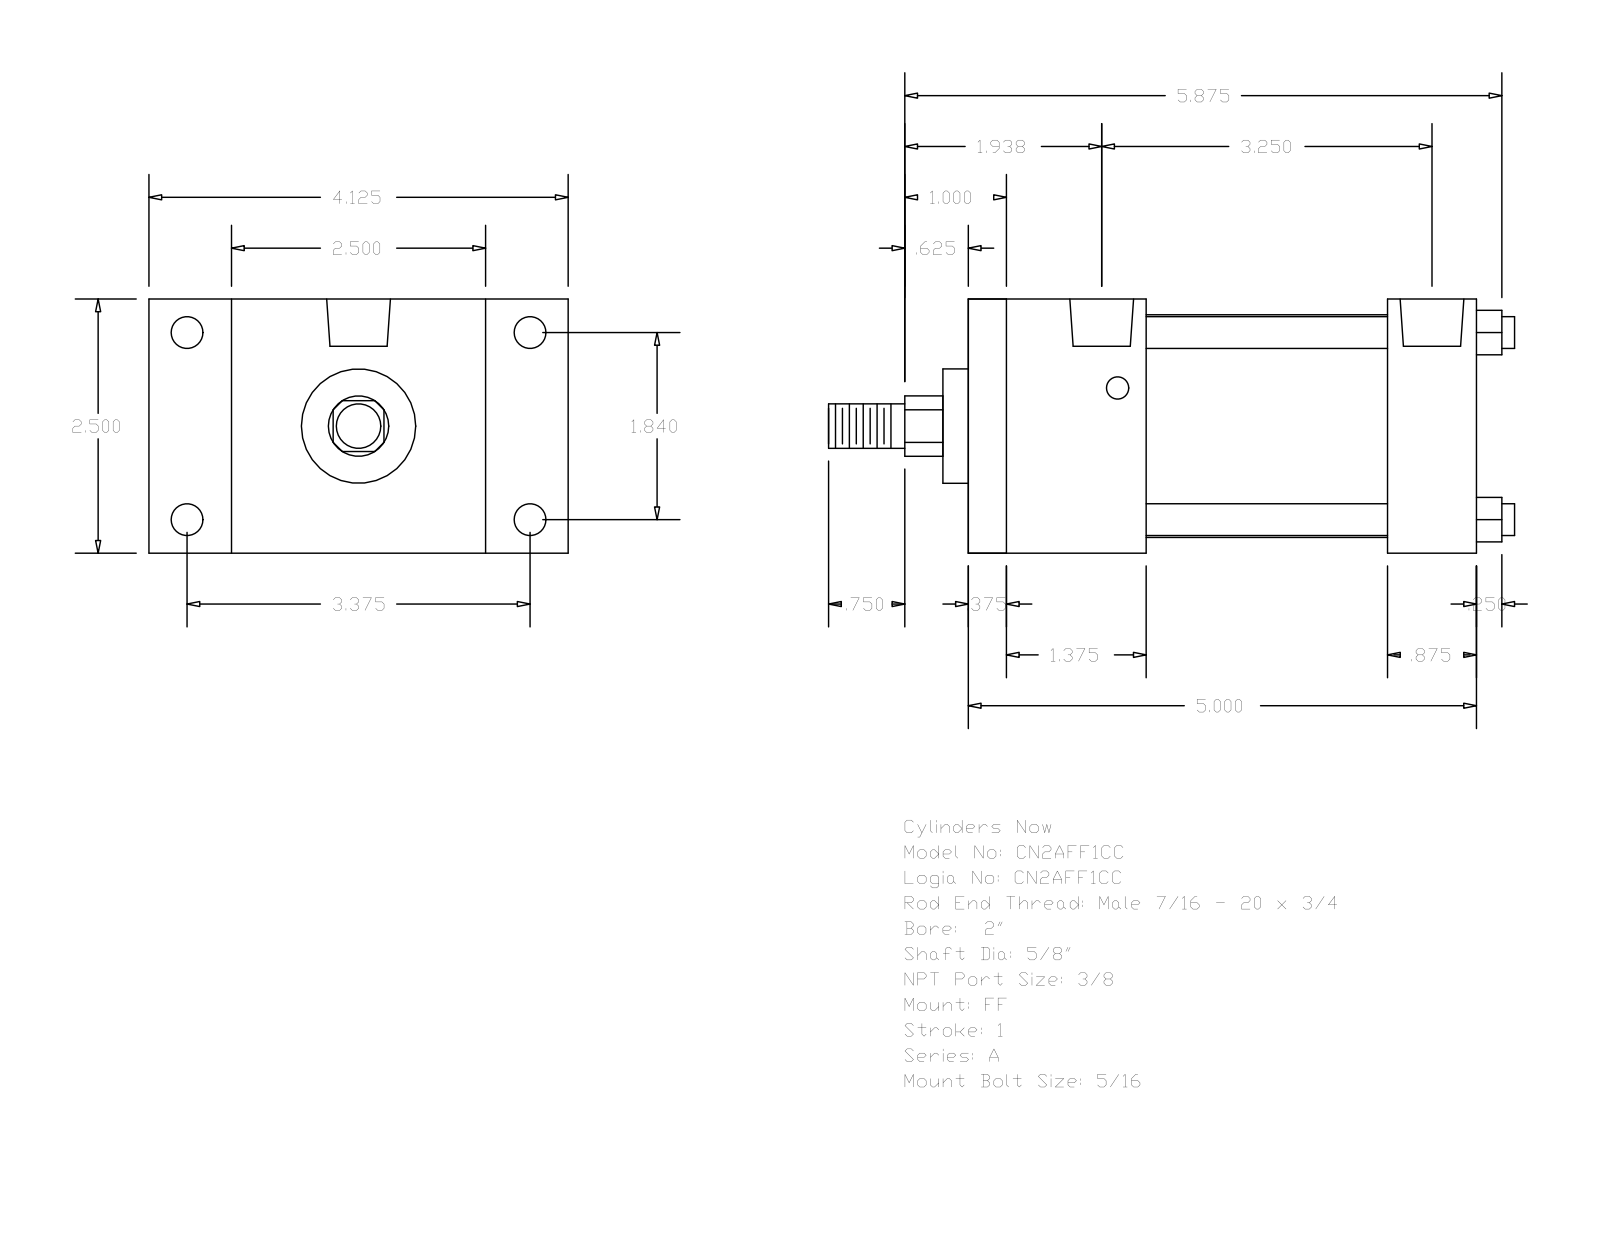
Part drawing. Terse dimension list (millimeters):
name: A_FF__0200_0.625
written by: GSSL Pune (CONFIG_CONTROL_DESIGN)
unit: mm
bodies: 0 solids, 92 faces (64 planar, 28 cylindrical, 0 other)
size: 171.45 × 104.78 × 63.5
holes: 4× ⌀5.56, 4× ⌀7.94, 2× ⌀15.93
bosses: 4× ⌀7.94, 1× ⌀55.63, 1× ⌀28.57, 1× ⌀15.88, 1× ⌀11.11
rounds: 1× R7.54
face distances: 63.5, 127, 9.52, 117.48, 34.93, 44.45, 104.77, 95.25, 60.32, 82.55
hole spacings: 46.74, 74.6, 85.72, 97.63, 3.97, 3.98, 78.57, 78.58
